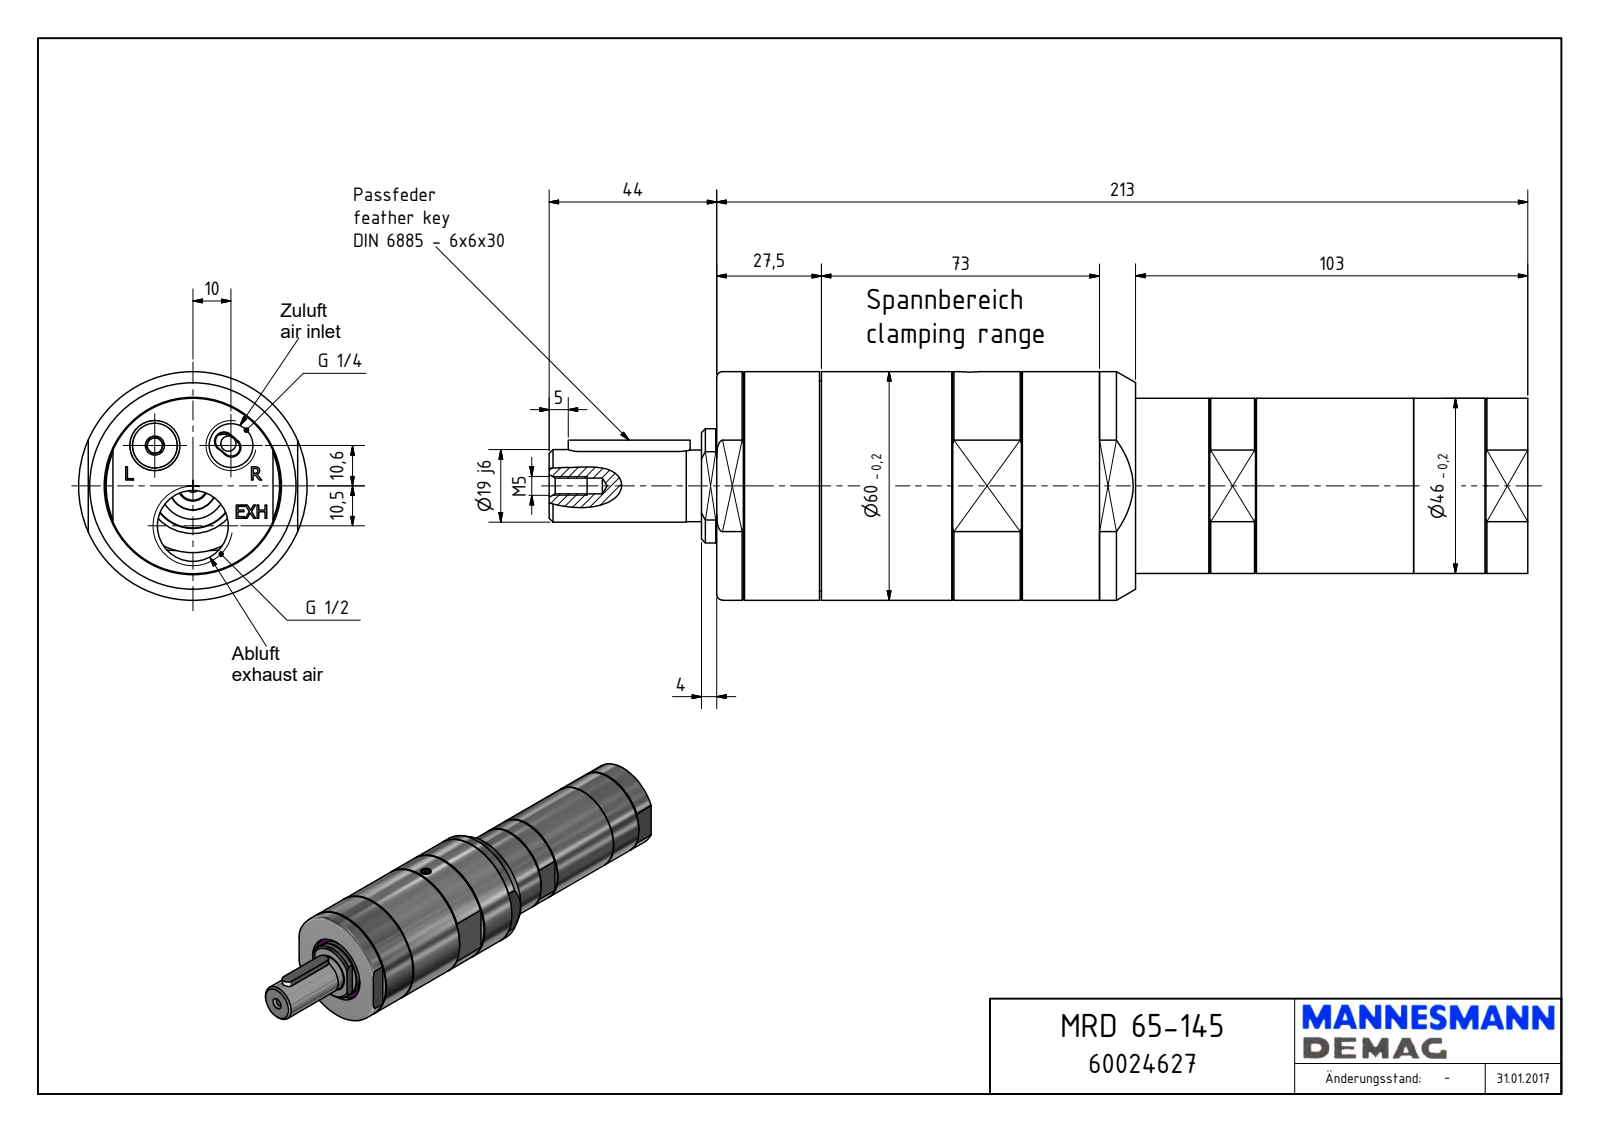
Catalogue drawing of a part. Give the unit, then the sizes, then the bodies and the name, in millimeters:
Units: millimetres
Overall size (bounding box): 257 × 60 × 60
Round holes (diameter × count): ⌀4 ×2, ⌀1.55 ×1, ⌀4.13 ×1, ⌀5.5 ×1, ⌀11.45 ×1, ⌀18.63 ×1, ⌀35 ×1, ⌀46.5 ×1, ⌀55.38 ×1
Round bosses / shafts (diameter × count): ⌀60 ×1, ⌀55.18 ×1, ⌀46 ×1, ⌀41.91 ×1, ⌀40 ×1, ⌀33.32 ×1, ⌀29.95 ×1, ⌀19 ×1
Partial cylindrical surfaces — rounded edges, fillets, slot ends (radius × count): R2.5 ×4, R3 ×2, R5 ×2, R5.72 ×1, R16.75 ×1, R19 ×1, R25.27 ×1
Main face-to-face distances: 6.5, 213, 48.5, 55, 103, 110, 185.5, 103.43, 6.57, 109.57
Hole centre spacings: 14.57, 23.35, 10.5, 20
Volume: 486 460 mm³ · Surface area: 50 542 mm²
Bodies: 1 solid, 234 faces (131 planar, 54 cylindrical, 49 other)
Part name (STEP PRODUCT): MRD 65-145_60024627
STEP written by: Autodesk Inventor 2018 (AUTOMOTIVE_DESIGN)
